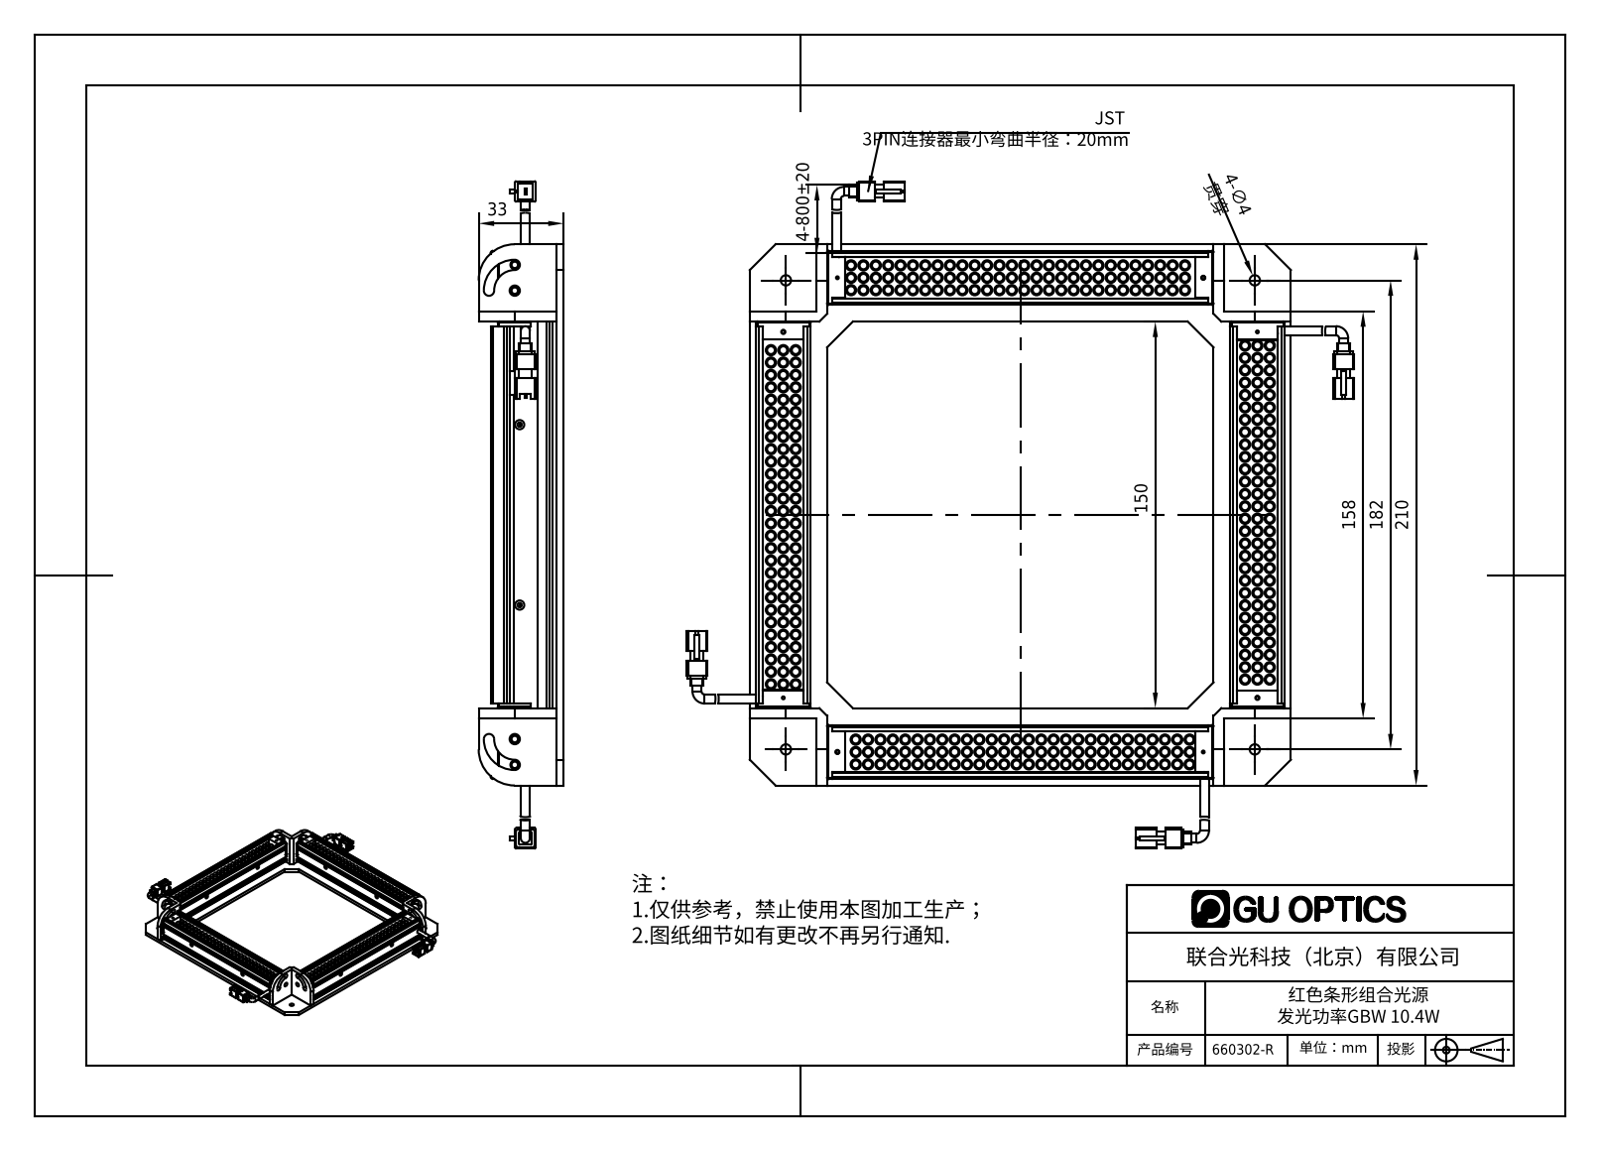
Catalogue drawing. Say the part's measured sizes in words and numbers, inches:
The part is named "660302-R". Its 3-D file was written by "SolidWorks 2016 (AUTOMOTIVE_DESIGN)". It is 29 solids with 3465 faces: 1176 planar, 1712 cylindrical and 577 other. Overall it measures 10.197 by 10.197 by 1.299 inches. Its volume is 14.55 cubic inches and its surface area 333.4 square inches. Round holes: 12 of diameter 0.063, 8 of diameter 0.098, 8 of diameter 0.118, 8 of diameter 0.157, 4 of diameter 0.043, 4 of diameter 0.049, 4 of diameter 0.067, 4 of diameter 0.079. Round bosses or shafts: 336 of diameter 0.157, 336 of diameter 0.118, 8 of diameter 0.138. Partial cylindrical surfaces (rounded edges, fillets, slot ends): 48 of radius 0.039, 32 of radius 0.02, 8 of radius 0.079, 4 of radius 0.065, 4 of radius 0.315, 4 of radius 0.472, 4 of radius 0.551. The main face-to-face distances are 0.098, 0.118, 7.244, 0.728, 0.827, 0.157, 0.039, 7.146, 0.39, 0.256. The hole center spacings are 0.645, 0.788, 1.033, 5.591, 6.222, 6.378, 6.47, 6.616.
